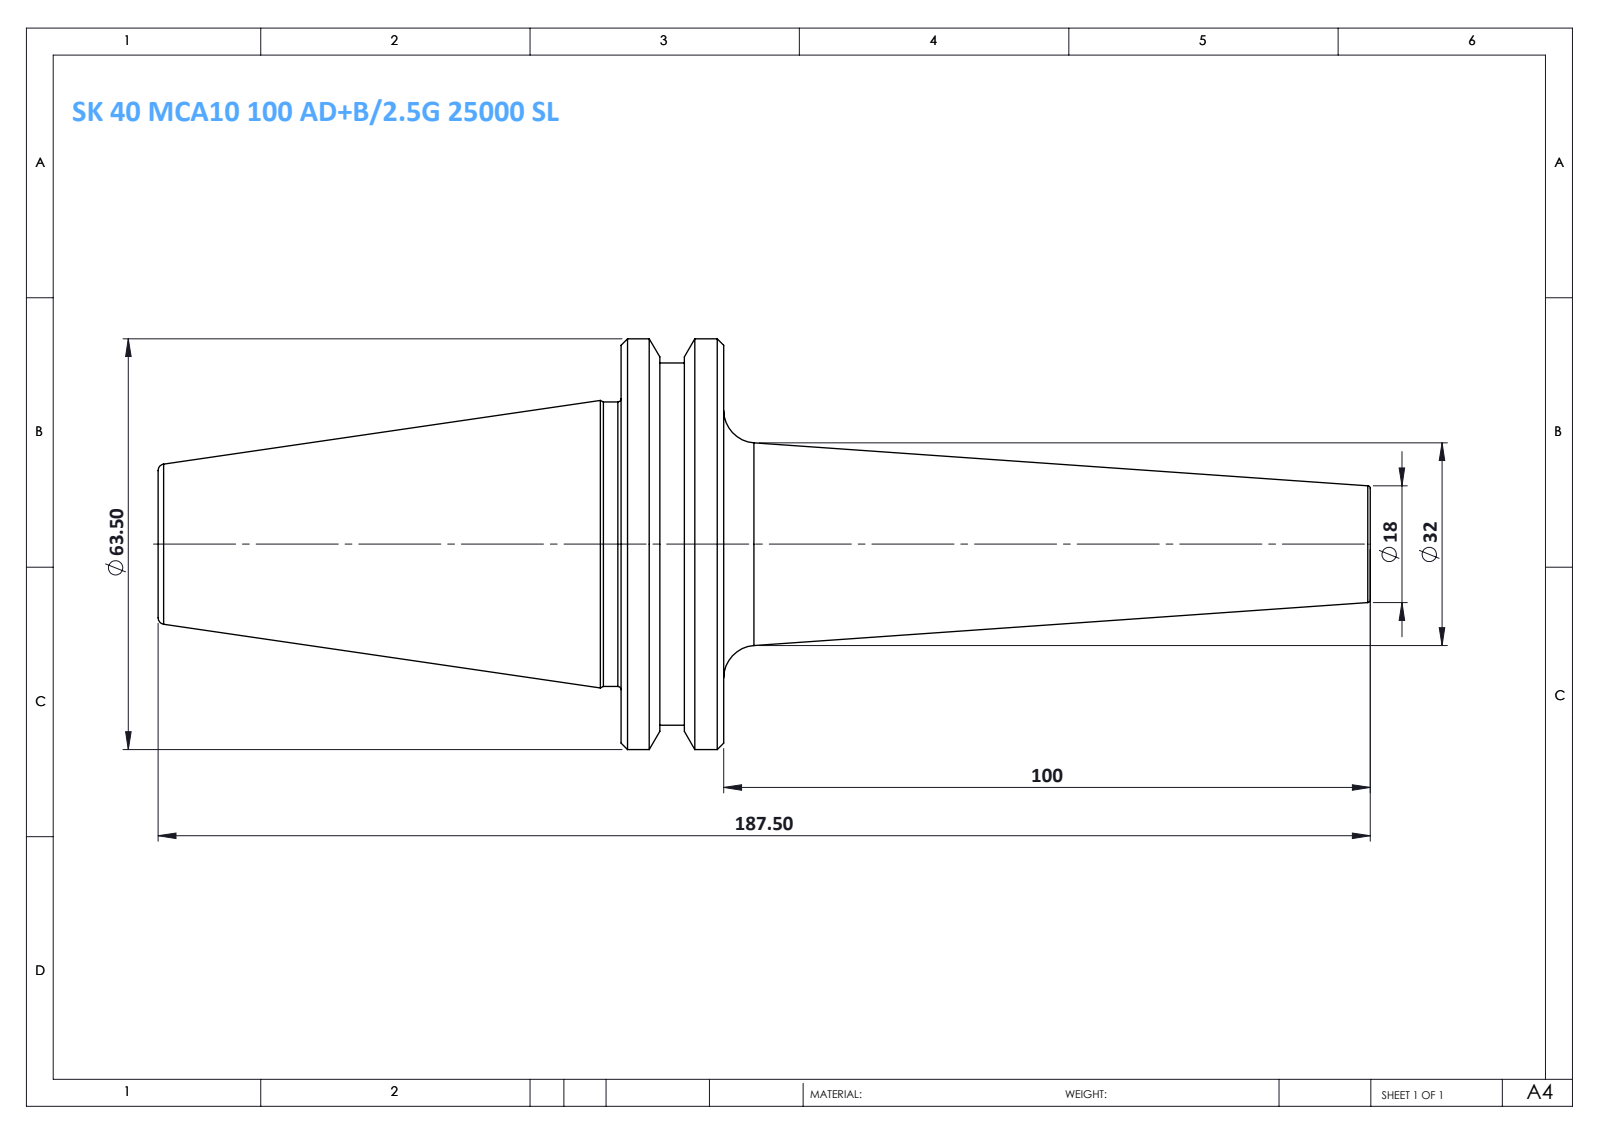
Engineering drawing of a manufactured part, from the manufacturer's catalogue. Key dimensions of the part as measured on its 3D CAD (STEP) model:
Part name (STEP PRODUCT): SK 40 MCA10 100 AD+B-2.5G 25000 SL
STEP written by: SolidWorks 2014 (CONFIG_CONTROL_DESIGN)
Units: millimetres
Bodies: 1 solid, 36 faces (6 planar, 8 cylindrical, 22 other)
Overall size (bounding box): 187.5 × 63.5 × 63.5
Volume: 167 961 mm³ · Surface area: 24 084 mm²
Round bosses / shafts (diameter × count): ⌀63.5 ×1, ⌀56 ×1, ⌀44 ×1
Main face-to-face distances: 15.9, 87.5, 71.6, 100, 115.9, 187.5, 106.1, 6.1, 9.8, 81.4
